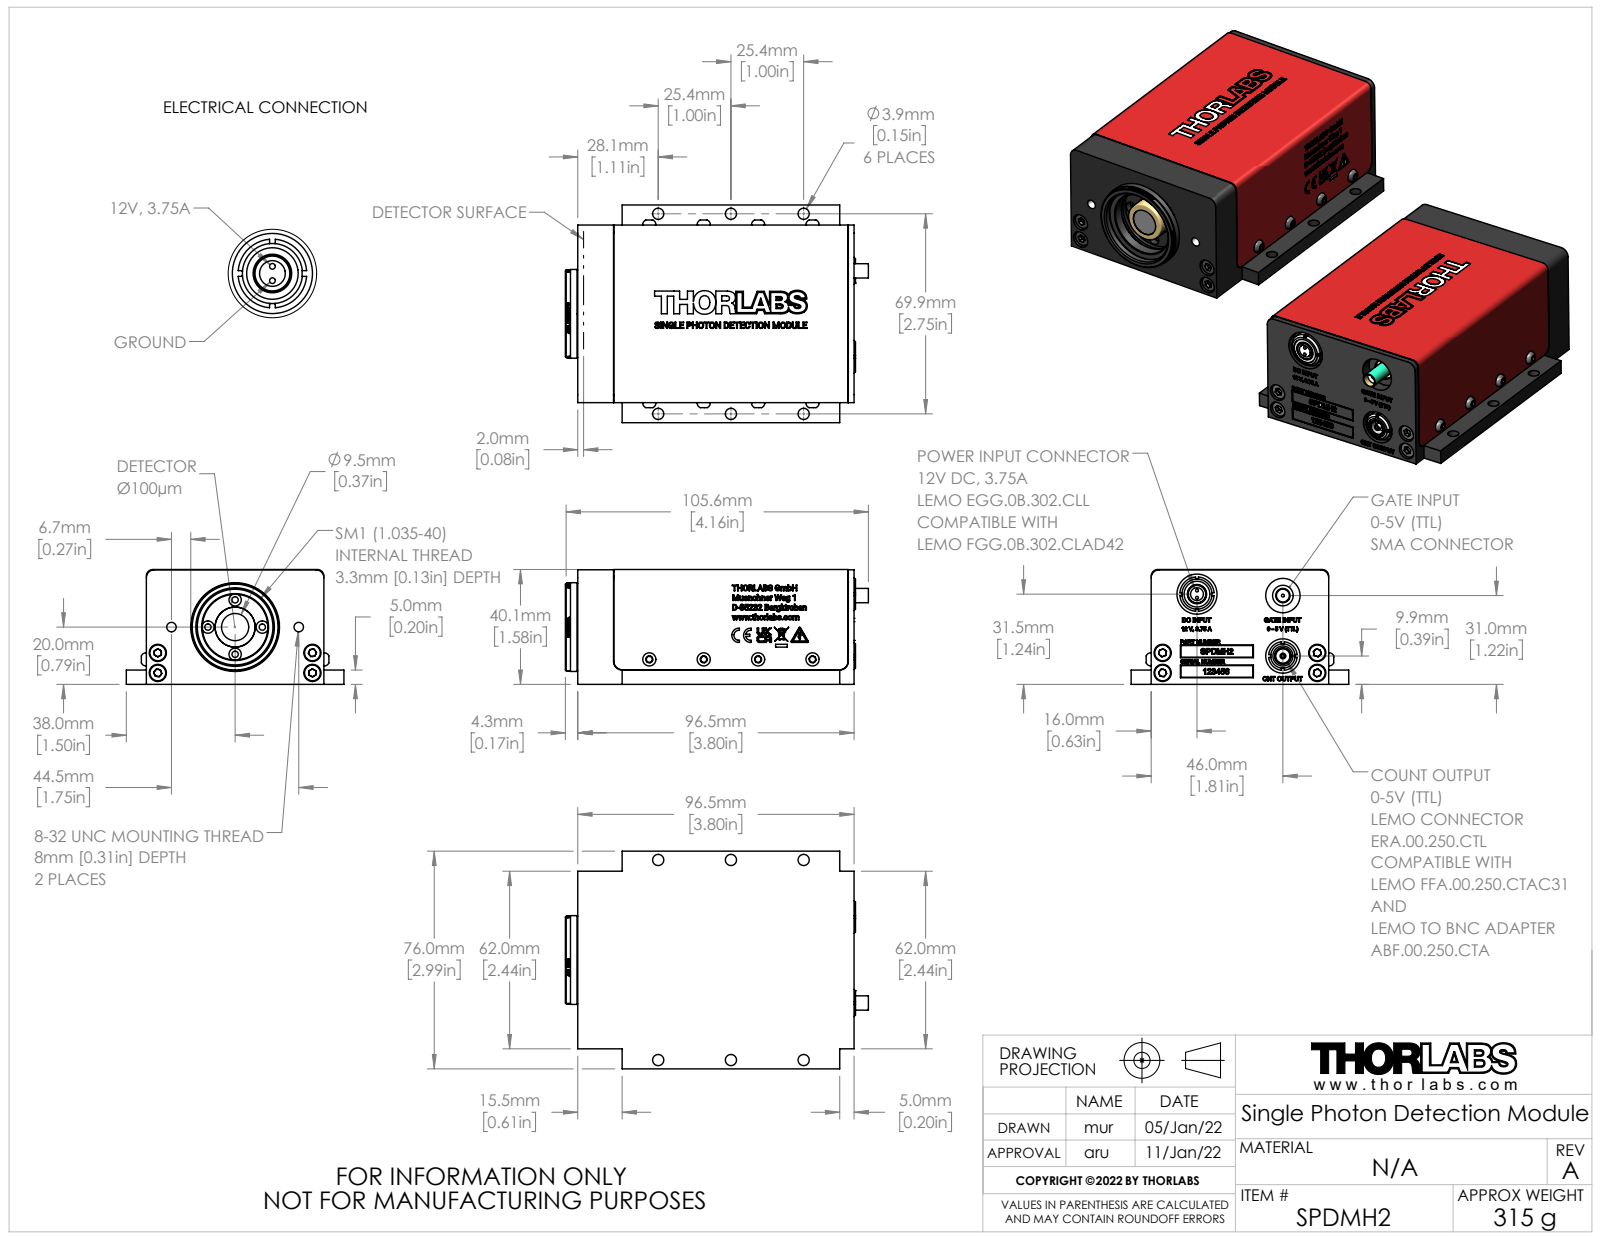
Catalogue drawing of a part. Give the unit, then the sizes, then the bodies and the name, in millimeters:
Units: millimetres
Overall size (bounding box): 105.8 × 76 × 40.1
Round holes (diameter × count): ⌀3.9 ×6, ⌀1 ×4, ⌀2 ×4, ⌀2.2 ×4, ⌀2.5 ×4, ⌀3.2 ×4, ⌀4.3 ×4, ⌀6 ×4, ⌀2 ×2, ⌀2 ×2, ⌀3.3 ×2, ⌀7.2 ×2
Round bosses / shafts (diameter × count): ⌀5.5 ×4, ⌀3 ×4, ⌀31 ×1, ⌀30.5 ×1, ⌀30.4 ×1, ⌀25.4 ×1, ⌀24.9 ×1, ⌀14 ×1
Partial cylindrical surfaces — rounded edges, fillets, slot ends (radius × count): R0.2 ×6, R0.7 ×6, R1.2 ×4, R1.4 ×4, R3 ×4, R0.2 ×3, R0.3 ×3, R0.8 ×3
Main face-to-face distances: 0.8, 5, 39.3, 34.3, 40.1, 35.1, 62, 61.2, 76, 15.5
Hole centre spacings: 19, 25.4, 9.5, 13.4, 24.2, 24.5, 29.2, 46
Bodies: 0 solids, 3323 faces (2412 planar, 260 cylindrical, 651 other)
Part name (STEP PRODUCT): 22.04.06_SPDMH2 WEB
STEP written by: SolidWorks 2019 (AUTOMOTIVE_DESIGN)
